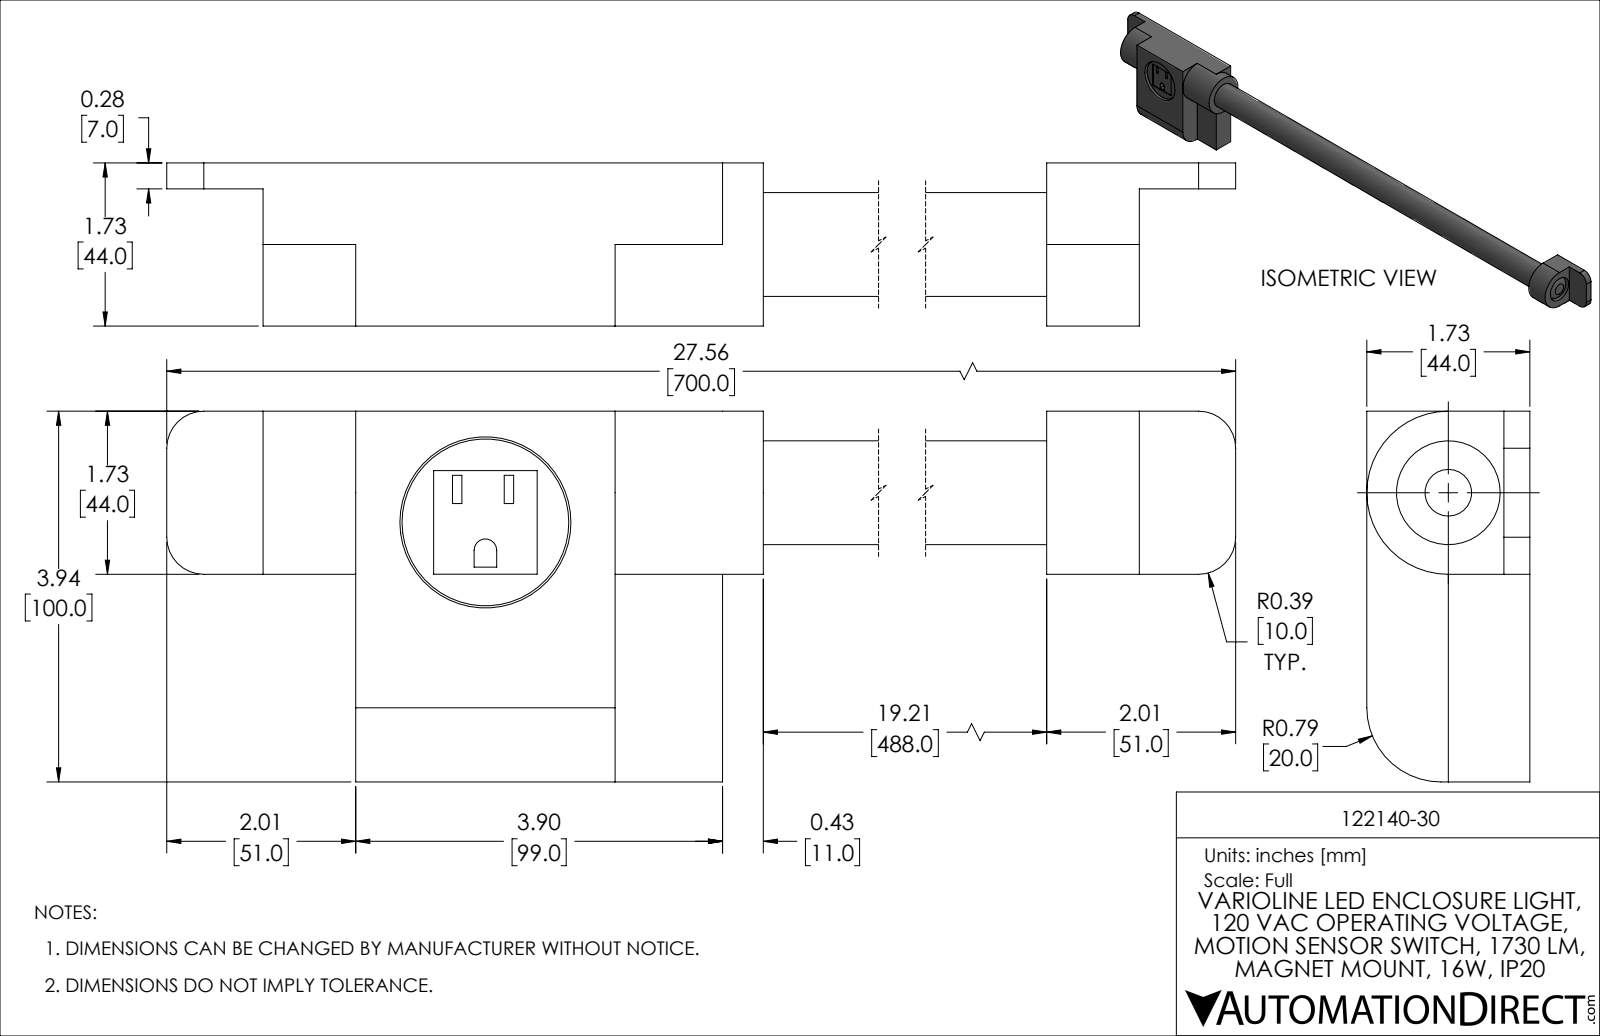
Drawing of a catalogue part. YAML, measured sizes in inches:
part_name: "PRODUCT_NAME_1"
step_written_by: "ACIS (AUTOMOTIVE_DESIGN_CC2)"
units: inches
bodies: {solids: 1, faces: 75, planar: 47, cylindrical: 22, other: 6}
overall_size: [27.559, 3.937, 1.732]
volume: 48.59
surface_area: 164.3
round_holes:
  - {diameter: 1.102, count: 1}
  - {diameter: 1.817, count: 1}
round_bosses_or_shafts:
  - {diameter: 1.772, count: 1}
  - {diameter: 1.732, count: 1}
partial_cylinders:
  - {radius: 0.394, count: 4}
  - {radius: 0.12, count: 1}
  - {radius: 0.787, count: 1}
face_to_face_distances: [1.732, 0.866, 3.937, 0.276, 1.457, 0.984, 24.528, 0.591, 3.898, 2.756]
